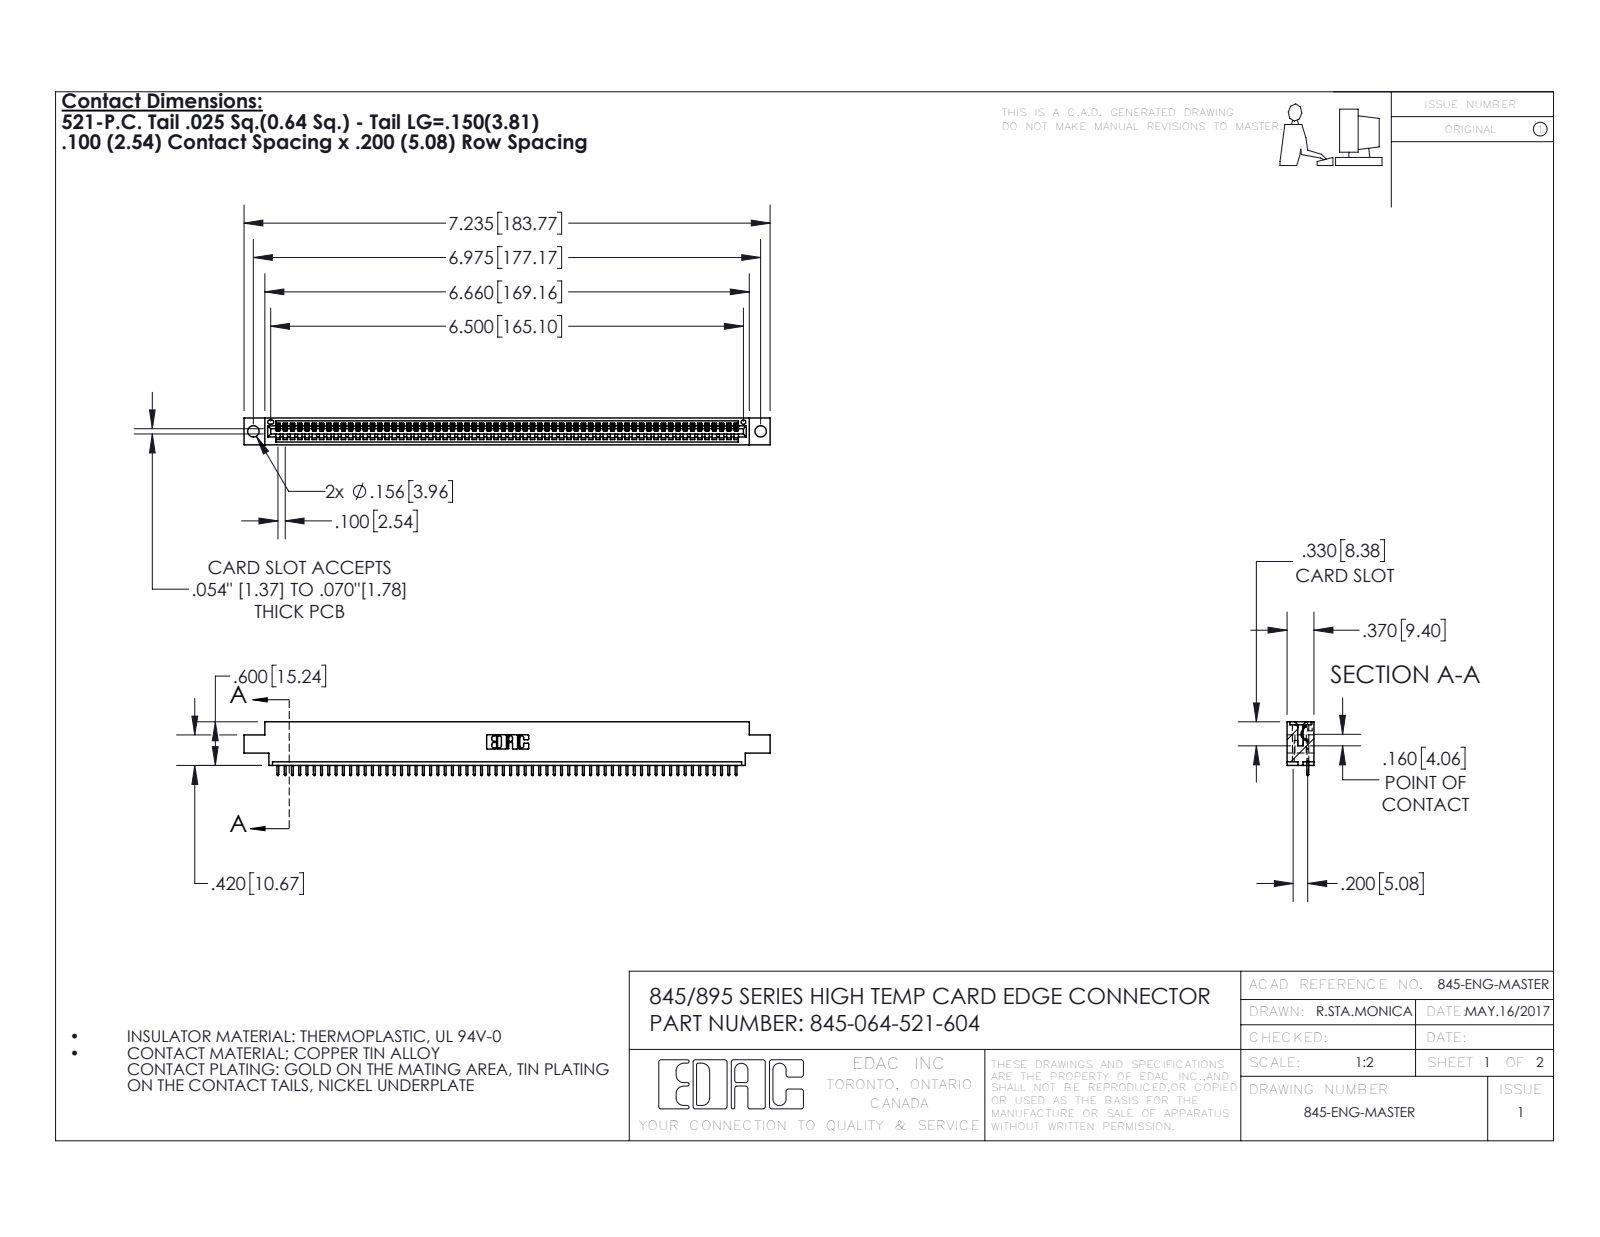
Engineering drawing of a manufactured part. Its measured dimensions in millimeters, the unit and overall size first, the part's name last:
Units: millimetres
Overall size (bounding box): 183.8 × 18.7 × 9.4
Round holes (diameter × count): ⌀4 ×2, ⌀1.6 ×1
Partial cylindrical surfaces — rounded edges, fillets, slot ends (radius × count): R0.2 ×128, R0.3 ×128, R0.3 ×22, R0.2 ×6, R0.8 ×6, R0.7 ×3, R0.8 ×2, R1 ×2
Main face-to-face distances: 7.6, 1.8, 9.4, 5.1, 2.5, 6.9, 0.6, 5.7, 4.4, 3.8
Hole centre spacings: 6.9, 171.2, 177.2
Volume: 17 260 mm³ · Surface area: 22 450 mm²
Bodies: 65 solids, 3842 faces (2644 planar, 1198 cylindrical, 0 other)
Part name (STEP PRODUCT): 345-064-521-604; 345 Part_0.170 Offset - 0.156 Dia-TH; 345-292-001_345-293-121
STEP written by: SolidWorks 2016 (CONFIG_CONTROL_DESIGN)
